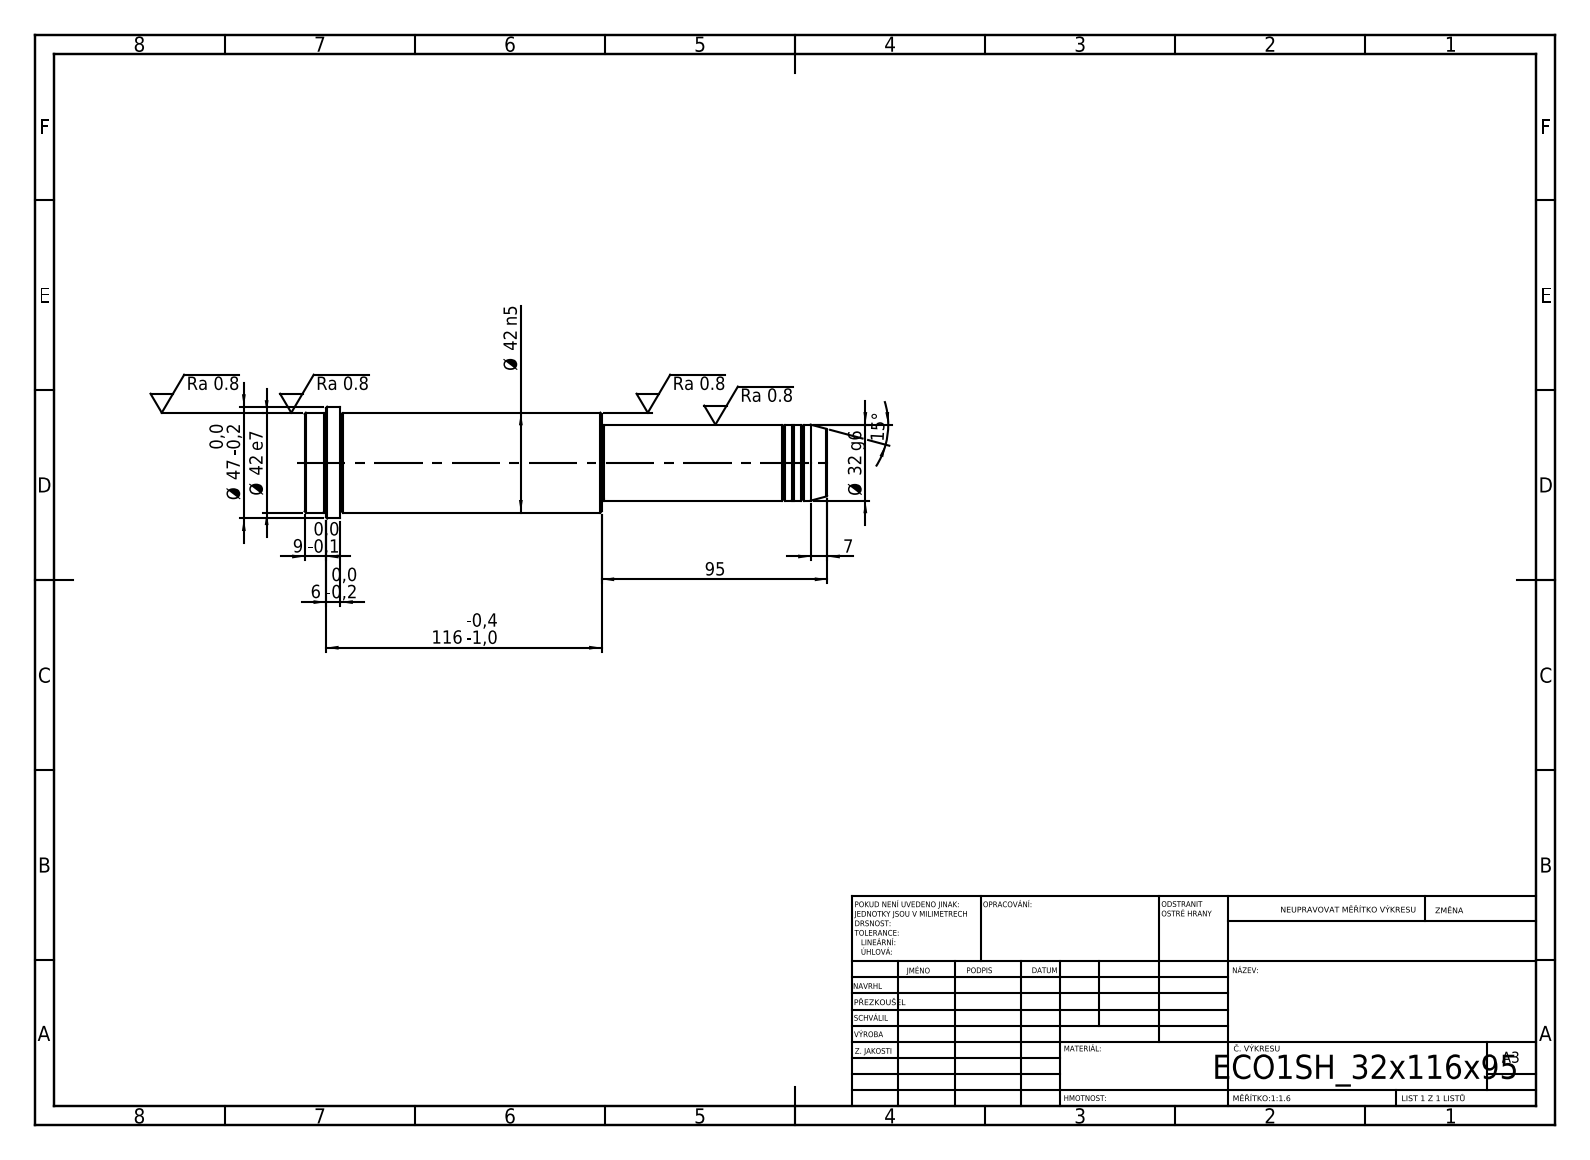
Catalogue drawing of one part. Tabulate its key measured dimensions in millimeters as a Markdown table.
| quantity | value |
| --- | --- |
| STEP written by | SolidWorks 2019 (CONFIG_CONTROL_DESIGN) |
| units | millimeters |
| bodies | 1 solid, 52 faces (6 planar, 16 cylindrical, 30 other) |
| overall size | 220 × 47 × 47 |
| volume | 250 724 mm³ |
| surface area | 29 684 mm² |
| round bosses / shafts (diameter × count) | 47 × 1, 42 × 1, 32 × 1, 31 × 1 |
| main face-to-face distances | 220, 95, 125, 205, 110, 15, 211, 116, 6, 9 |
